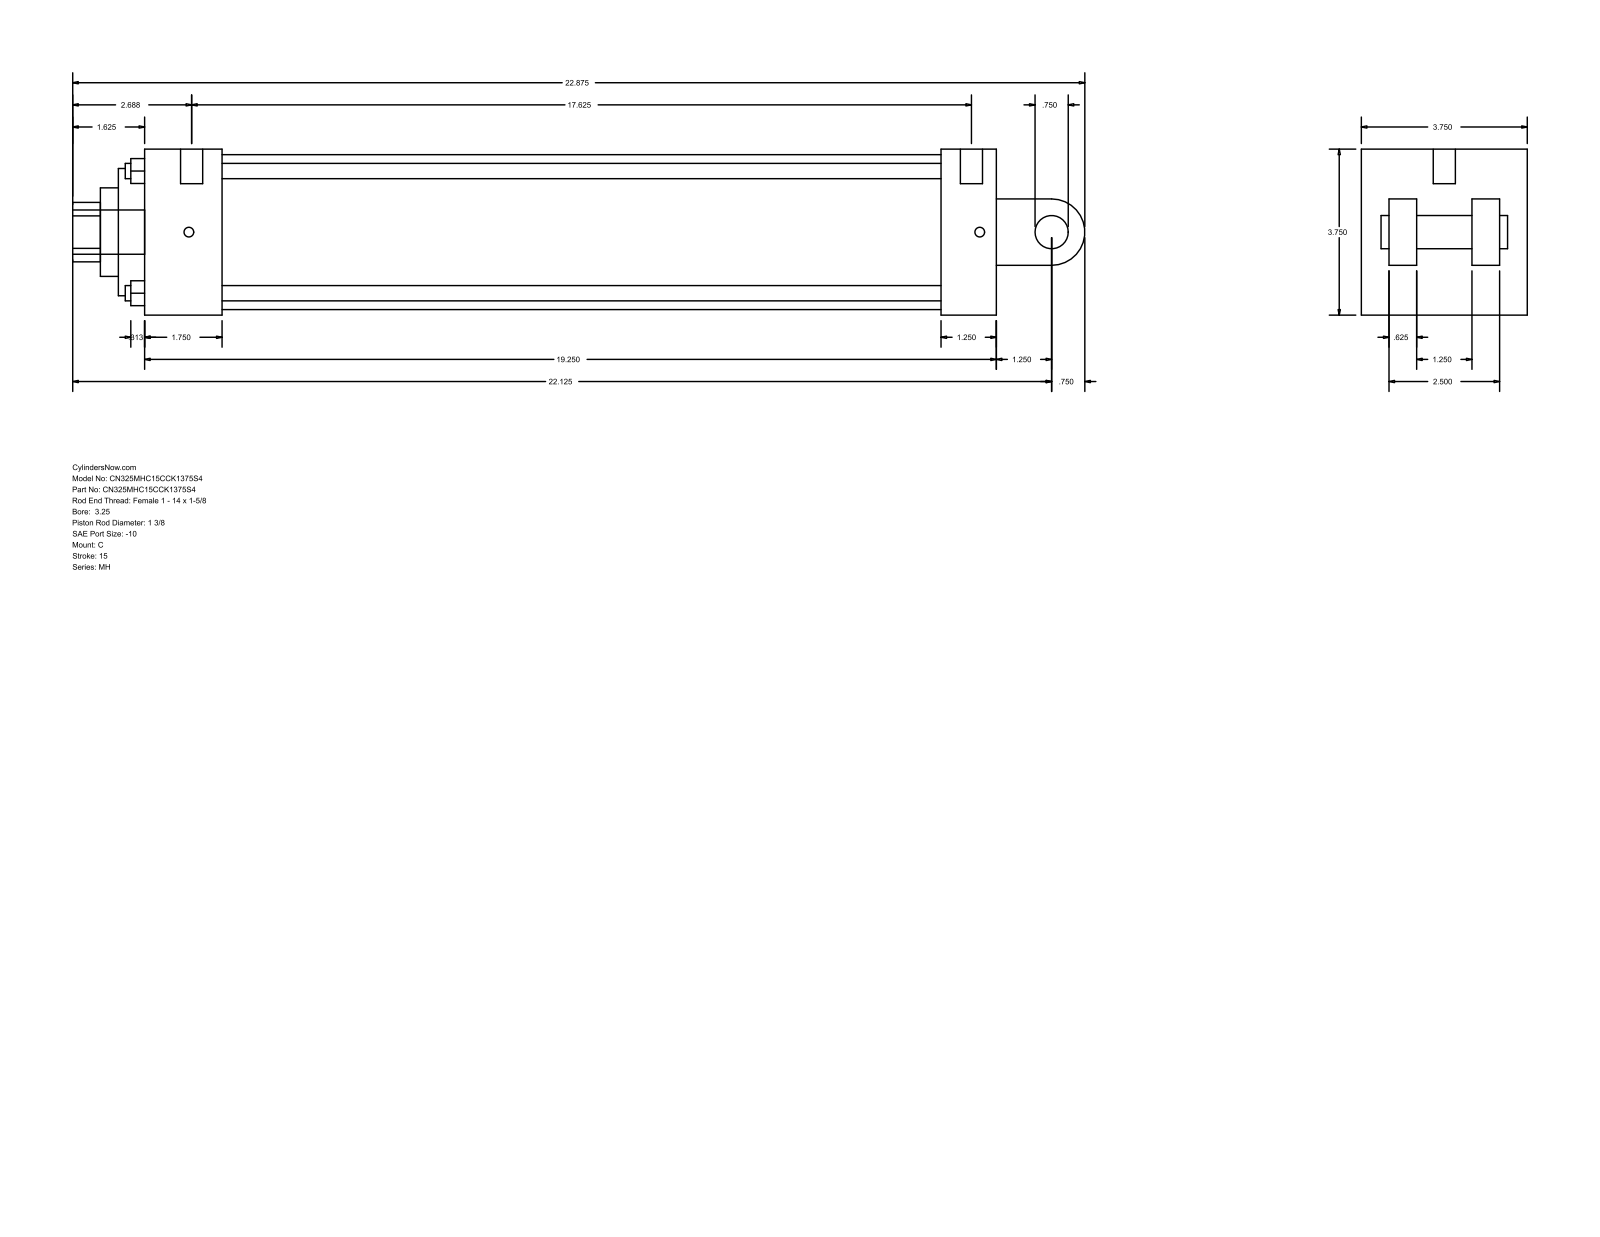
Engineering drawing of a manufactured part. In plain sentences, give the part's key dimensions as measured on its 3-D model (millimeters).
The part is named "MH_C__0325_1.375". Its 3-D file was written by "GSSL Pune (CONFIG_CONTROL_DESIGN)". It is 0 solids with 101 faces: 71 planar, 30 cylindrical and 0 other. Overall it measures 581.02 by 95.25 by 95.25 millimeters. Round holes: 4 of diameter 8.76, 2 of diameter 5.56, 1 of diameter 12.7, 1 of diameter 34.92, 1 of diameter 50.8, 1 of diameter 73.03, 1 of diameter 88.9. Round bosses or shafts: 2 of diameter 5.56, 1 of diameter 25.4, 1 of diameter 19.05, 1 of diameter 12.7. Partial cylindrical surfaces (rounded edges, fillets, slot ends): 1 of radius 17.06, 1 of radius 19.05. The main face-to-face distances are 95.24, 15.87, 488.96, 63.5, 31.74, 79.37, 47.63, 44.45, 457.21, 412.76. The hole center spacings are 49.57, 70.1, 99.14, 4.76.
